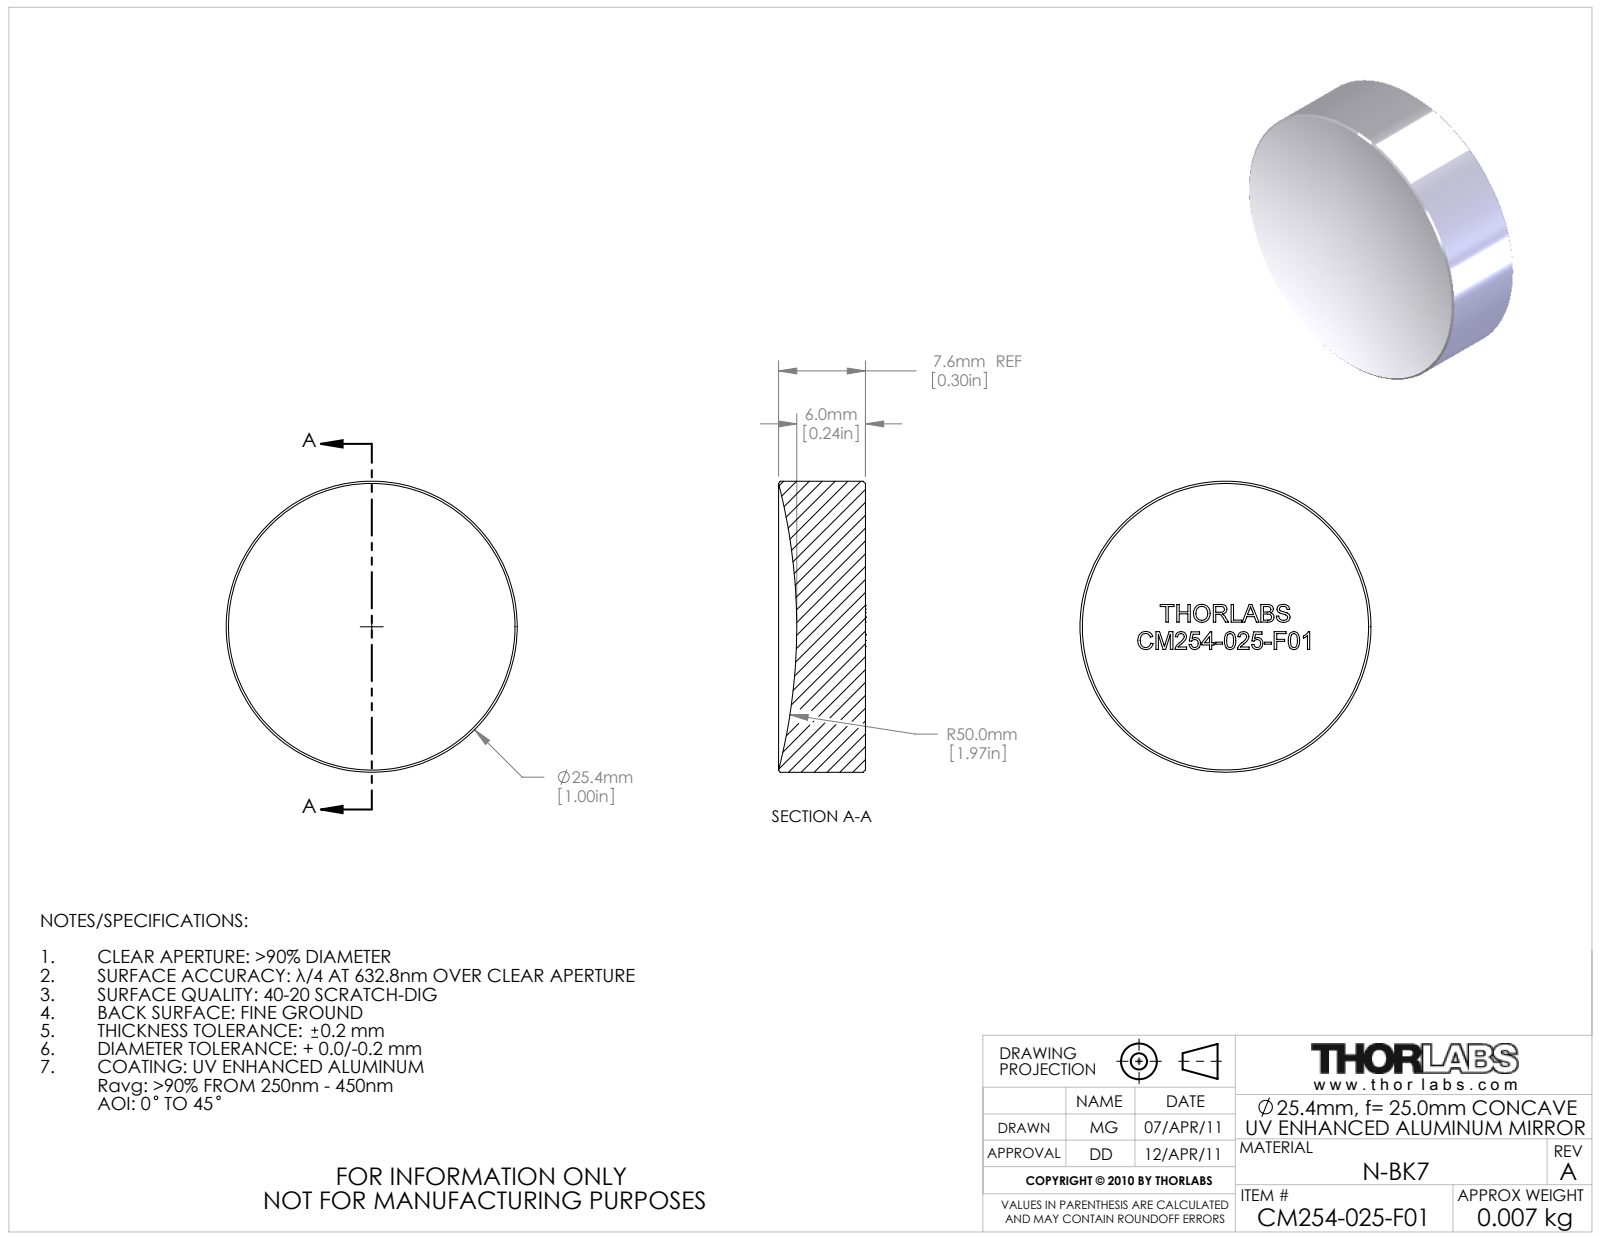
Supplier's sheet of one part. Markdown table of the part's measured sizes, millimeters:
| quantity | value |
| --- | --- |
| part name | 22194-E0W |
| STEP written by | SolidWorks 2011 (AUTOMOTIVE_DESIGN) |
| units | millimeters |
| bodies | 1 solid, 281 faces (163 planar, 2 cylindrical, 116 other) |
| overall size | 25.4 × 25.4 × 7.6 |
| volume | 3 460 mm³ |
| surface area | 1 610 mm² |
| round bosses / shafts (diameter × count) | 25.4 × 1 |
| main face-to-face distances | 1.5, 2.4, 1.9, 1.5, 1.3, 0.9, 4.1, 0.9, 2.4, 0.6 |
